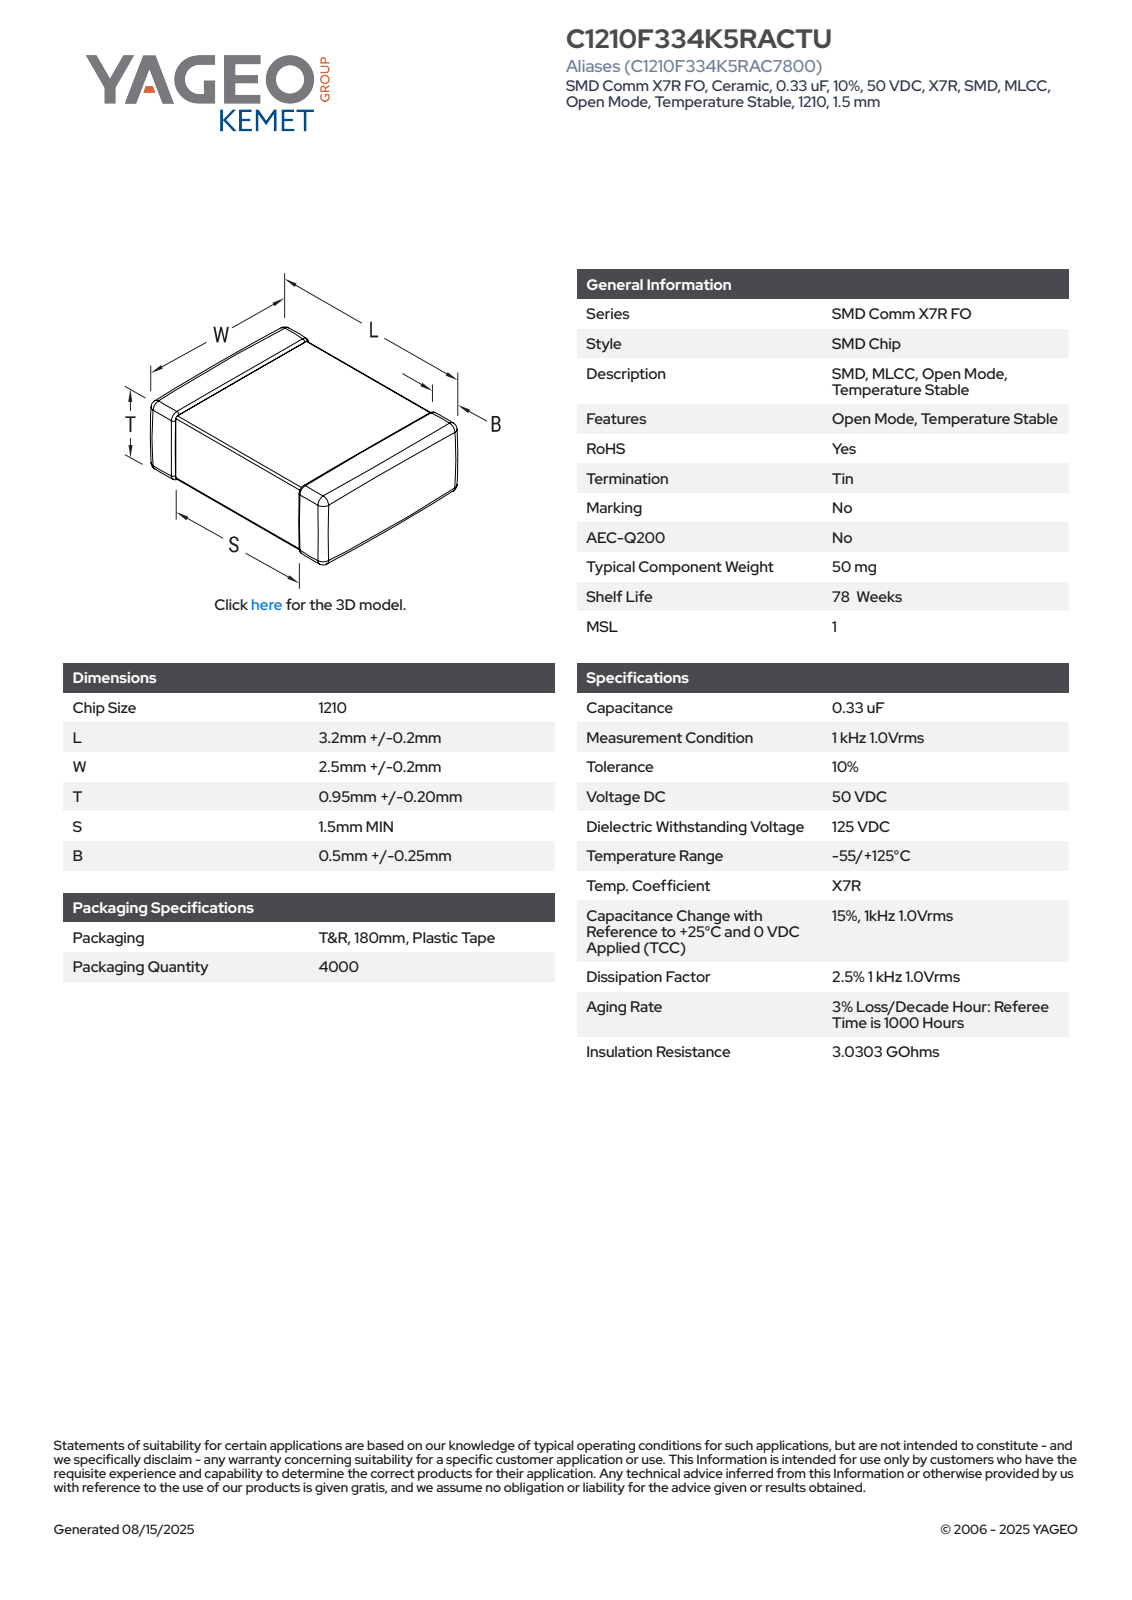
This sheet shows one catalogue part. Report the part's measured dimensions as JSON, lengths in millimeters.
{"part_name": "CCS_CCSTDNOS_1210_L3.4W2.7T1.15B0.75", "step_written_by": "SolidWorks 2014 (AUTOMOTIVE_DESIGN)", "units": "millimeters", "bodies": {"solids": 4, "faces": 125, "planar": 71, "cylindrical": 38, "other": 16}, "overall_size": [3.4, 2.7, 1.15], "volume_mm3": 10, "surface_area_mm2": 32, "face_to_face_distances": [1.09, 1.03, 1.15, 3.4, 2.64, 2.58, 2.7, 1.1, 1.04, 1.31]}
